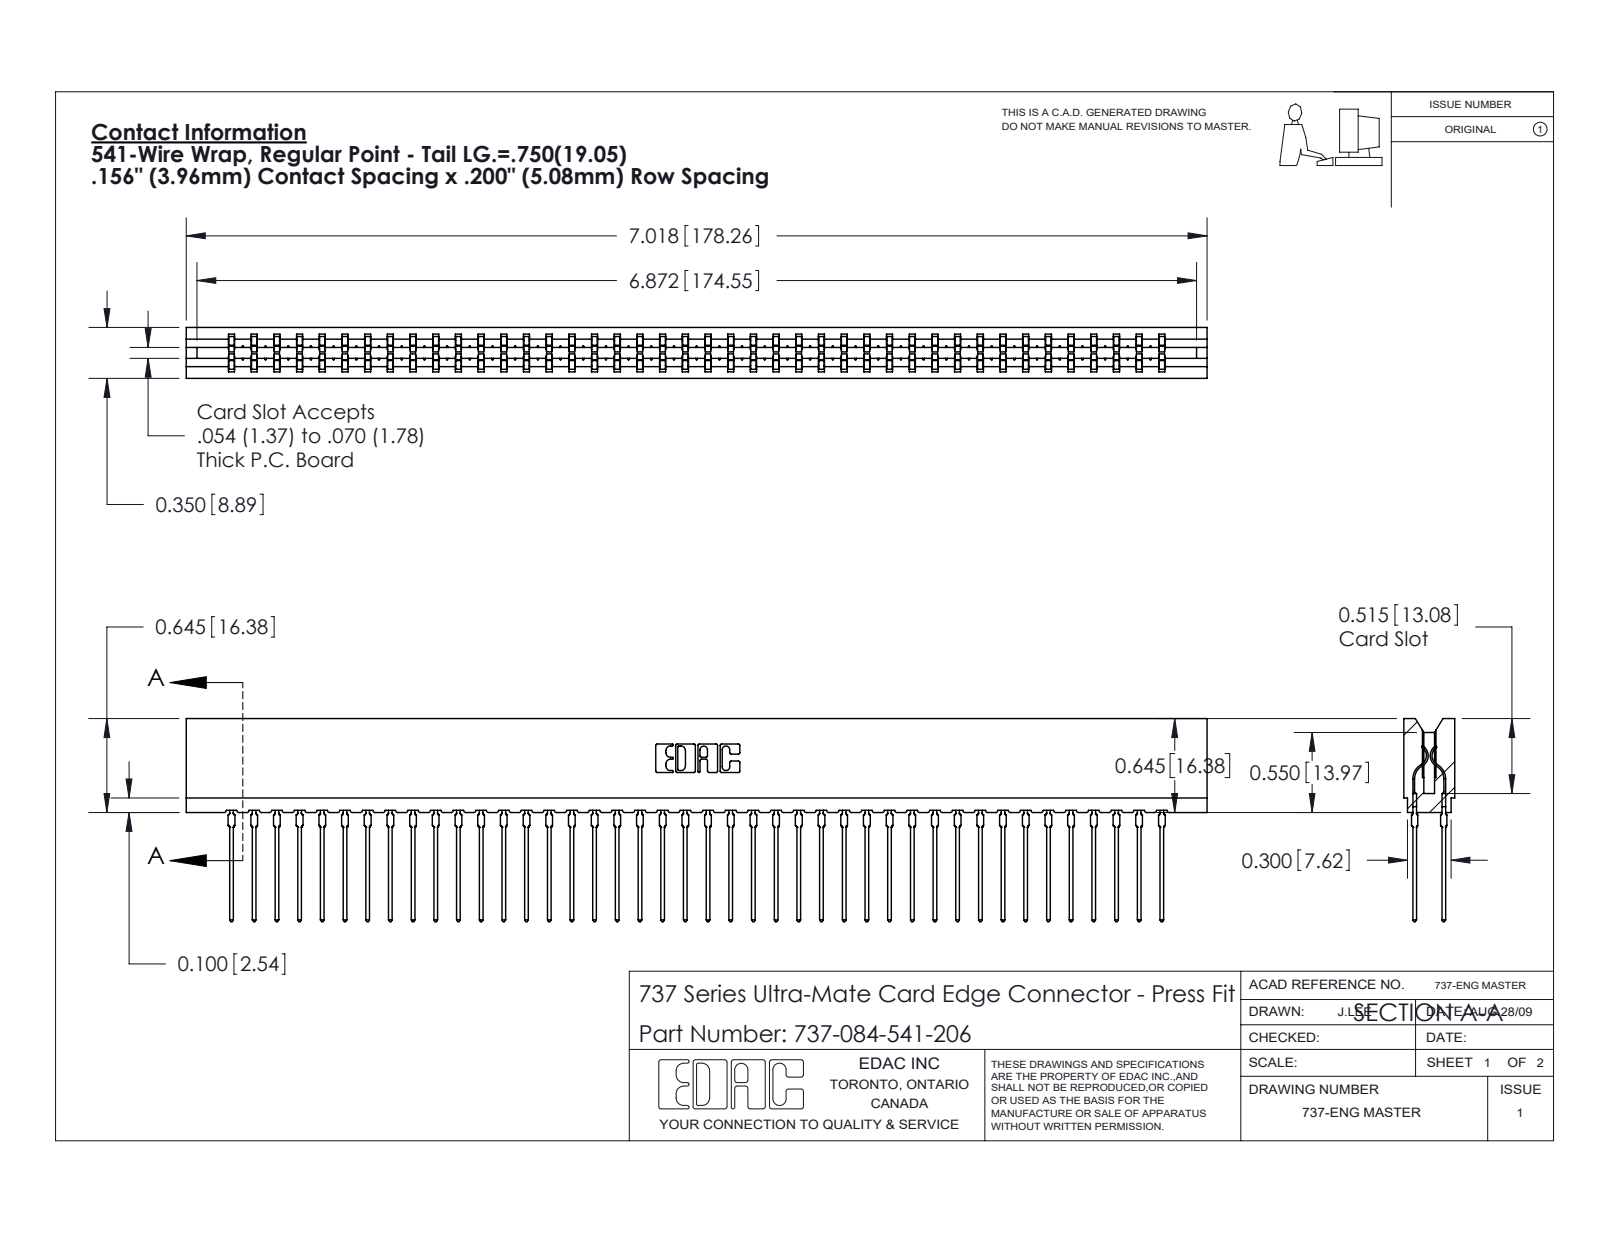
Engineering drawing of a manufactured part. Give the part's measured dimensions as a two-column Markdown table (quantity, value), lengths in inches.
| quantity | value |
| --- | --- |
| part name | 745-292-001_541; 737-084-541-206; 737 Part_Insulator Option - 06 |
| STEP written by | SolidWorks 2020 (CONFIG_CONTROL_DESIGN) |
| units | inches |
| bodies | 85 solids, 7655 faces (3961 planar, 1510 cylindrical, 2184 other) |
| overall size | 7.018 × 1.396 × 0.35 |
| volume | 1.099 in³ |
| surface area | 43.52 in² |
| partial cylindrical surfaces (radius × count) | 0.021 × 168, 0.015 × 84, 0.01 × 22, 0.005 × 8, 0.011 × 8, 0.007 × 6, 0.031 × 6, 0.026 × 3 |
| main face-to-face distances | 0.138, 0.212, 0.35, 0.063, 0.287, 0.076, 0.149, 0.074, 0.2, 0.087 |
